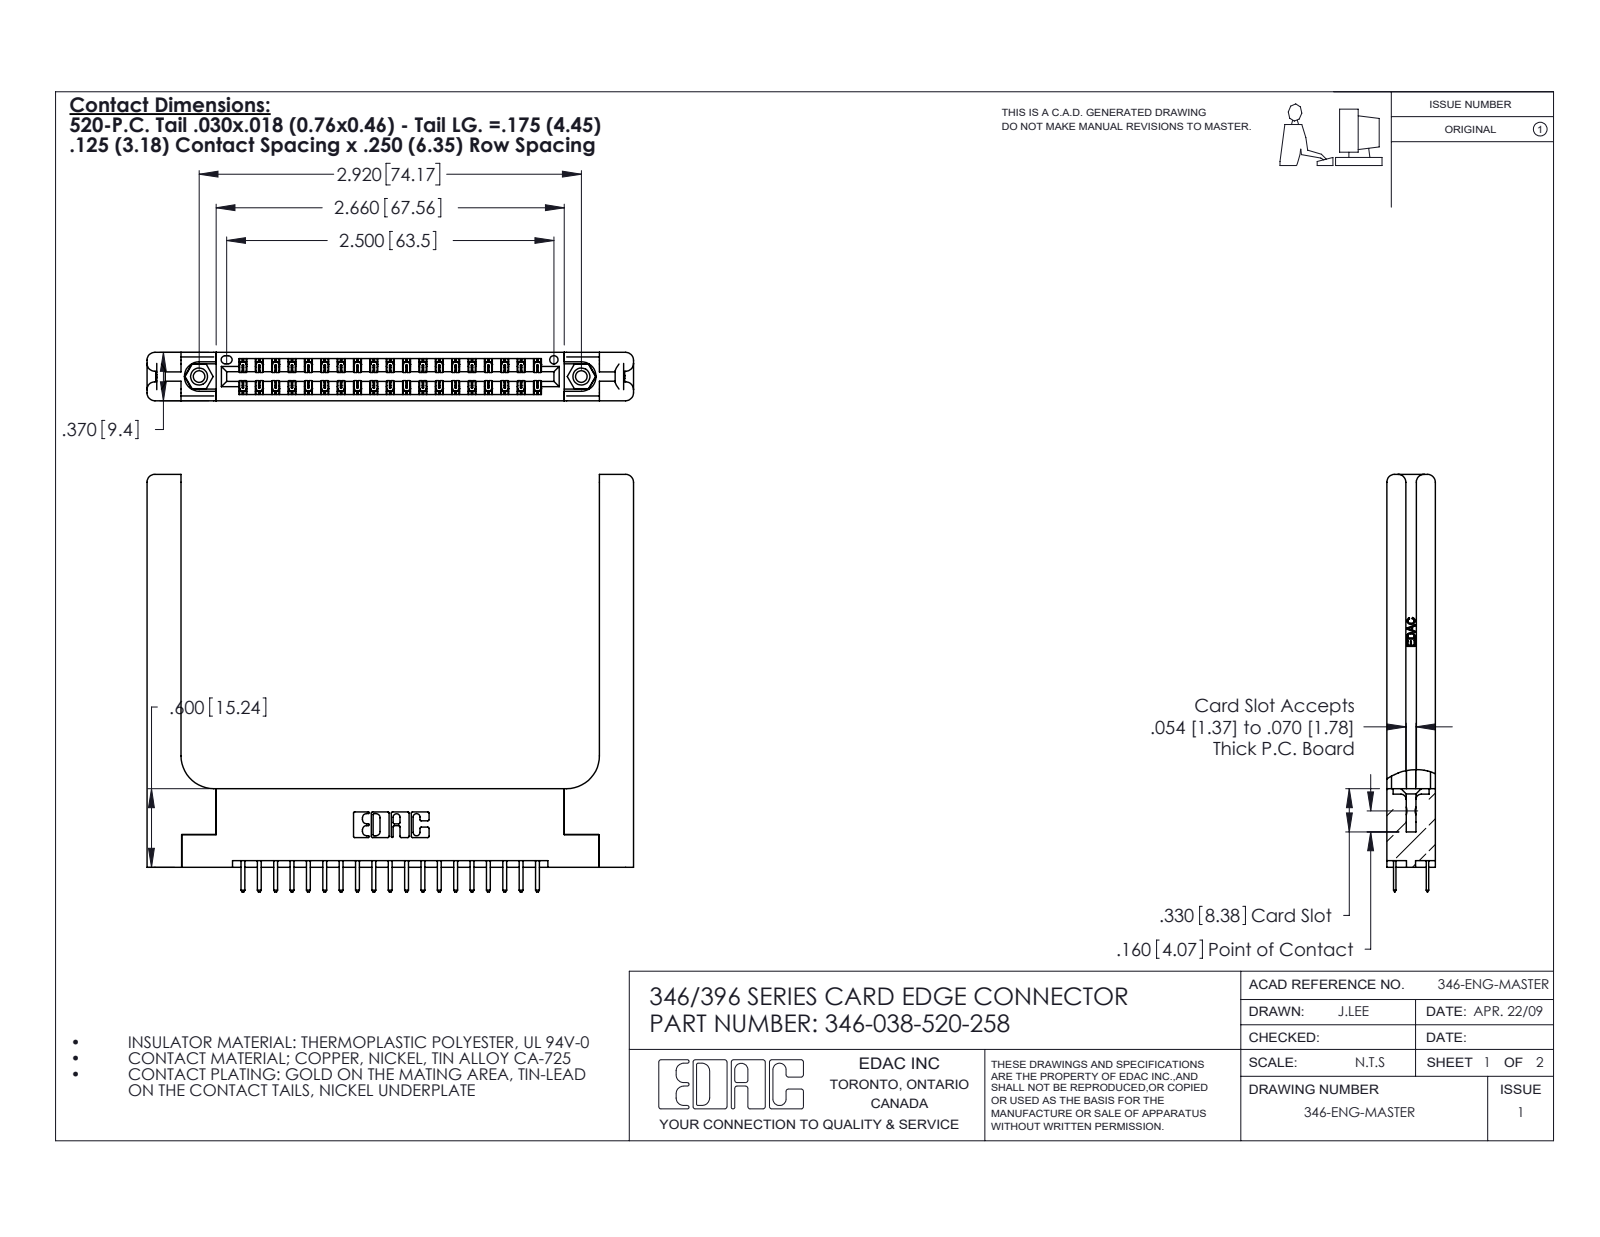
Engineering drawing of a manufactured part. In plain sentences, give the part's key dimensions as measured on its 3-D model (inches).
The part is named "346-220-058_345-220-058; 345-292-001_345-293-120; 346-038-520-258; 345-250-001_345-250-001-102 (+1 more)". Its 3-D file was written by "SolidWorks 2020 (CONFIG_CONTROL_DESIGN)". It is 43 solids with 2520 faces: 1644 planar, 816 cylindrical and 60 other. Overall it measures 3.716 by 3.188 by 0.37 inches. Its volume is 1.006 cubic inches and its surface area 26.3 square inches. Round holes: 2 of diameter 0.089, 2 of diameter 0.125, 2 of diameter 0.156, 1 of diameter 0.064. Round bosses or shafts: 2 of diameter 0.155. Partial cylindrical surfaces (rounded edges, fillets, slot ends): 57 of radius 0.006, 42 of radius 0.01, 22 of radius 0.01, 16 of radius 0.06, 6 of radius 0.007, 6 of radius 0.031, 3 of radius 0.026, 2 of radius 0.014. The main face-to-face distances are 0.37, 0.15, 0.072, 0.148, 0.048, 0.322, 0.25, 0.102, 0.22, 0.173. The hole center spacings are 0.246, 2.713, 2.92.
